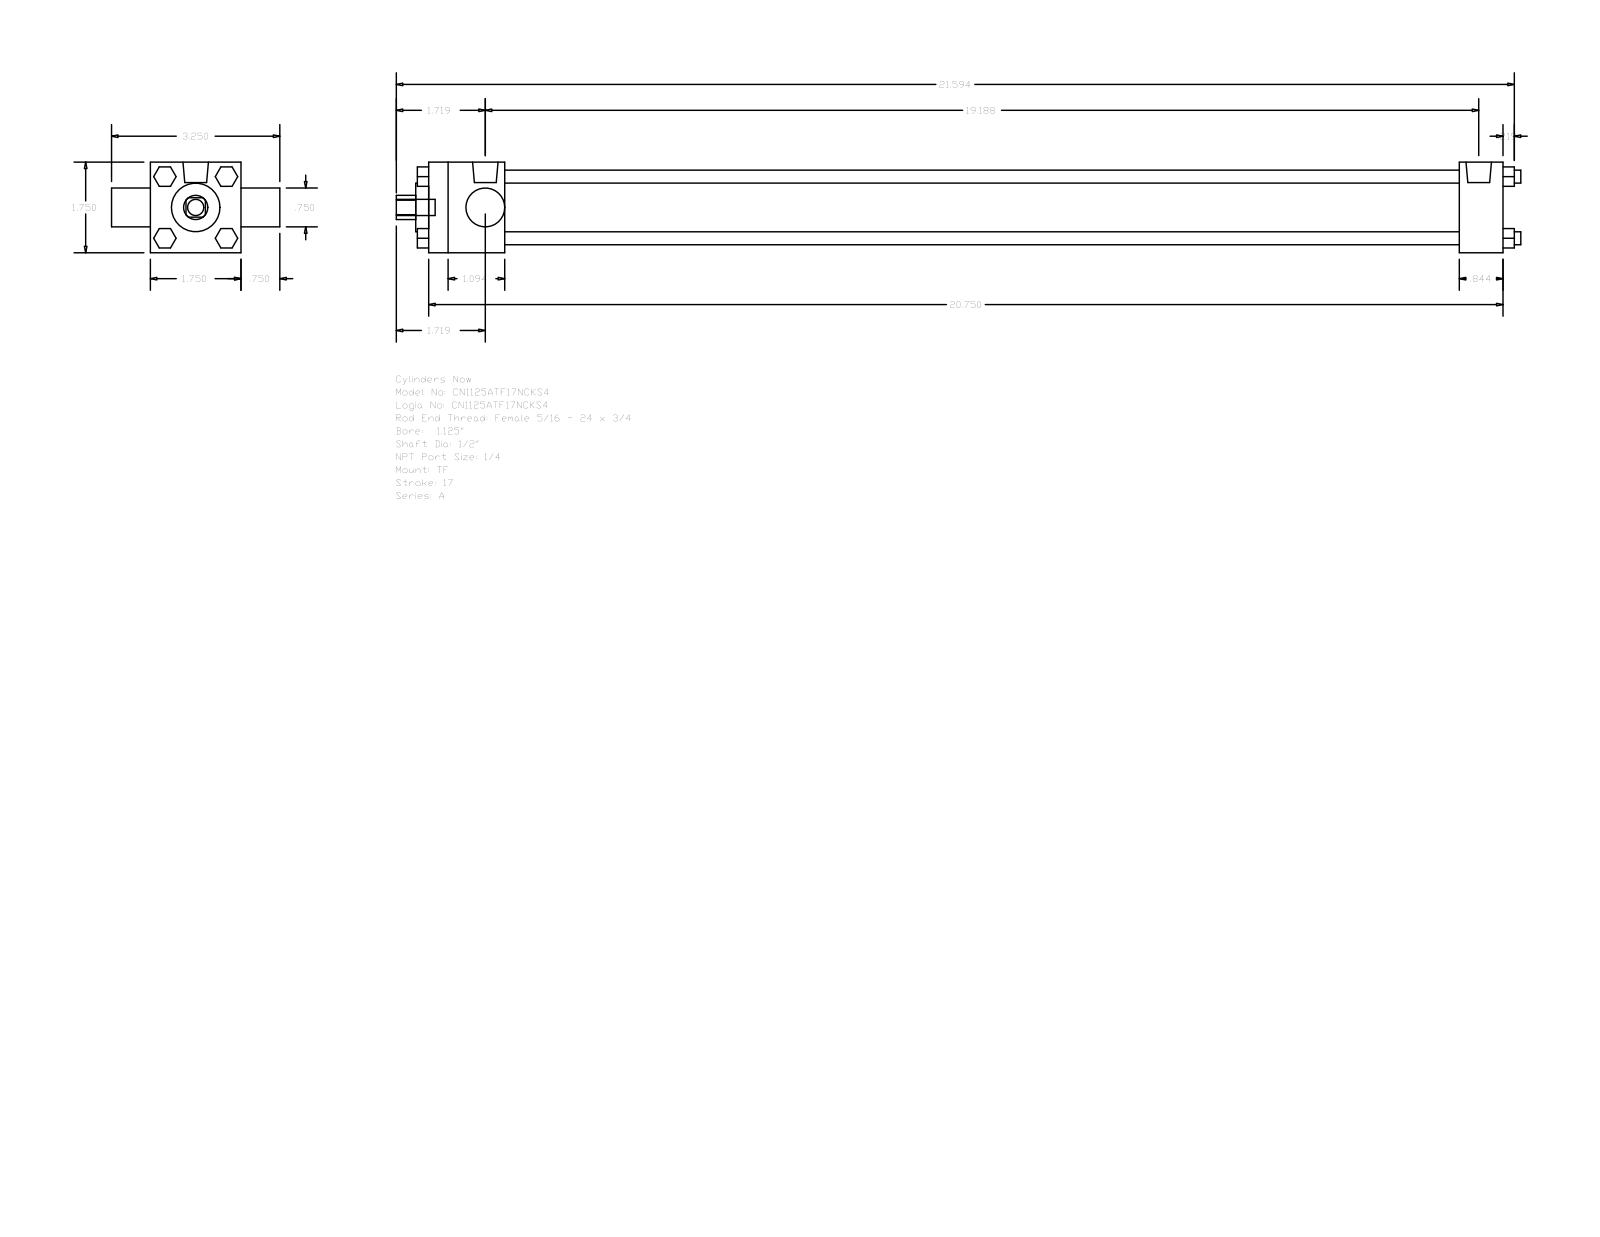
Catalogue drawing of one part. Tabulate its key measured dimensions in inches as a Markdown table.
| quantity | value |
| --- | --- |
| part name | A_TF__0112_0.5 |
| STEP written by | GSSL Pune (CONFIG_CONTROL_DESIGN) |
| units | inches |
| bodies | 0 solids, 120 faces (92 planar, 28 cylindrical, 0 other) |
| overall size | 21.719 × 3.25 × 1.75 |
| round holes (diameter × count) | 0.5 × 1, 0.75 × 1, 0.937 × 1, 1.255 × 1 |
| round bosses / shafts (diameter × count) | 0.25 × 4, 0.219 × 3, 0.492 × 2, 0.313 × 1 |
| partial cylindrical surfaces (radius × count) | 0.234 × 1 |
| main face-to-face distances | 1.75, 20.75, 19.906, 0.844, 1.469, 18.437, 19.281, 0.75, 2.5, 0.375 |
